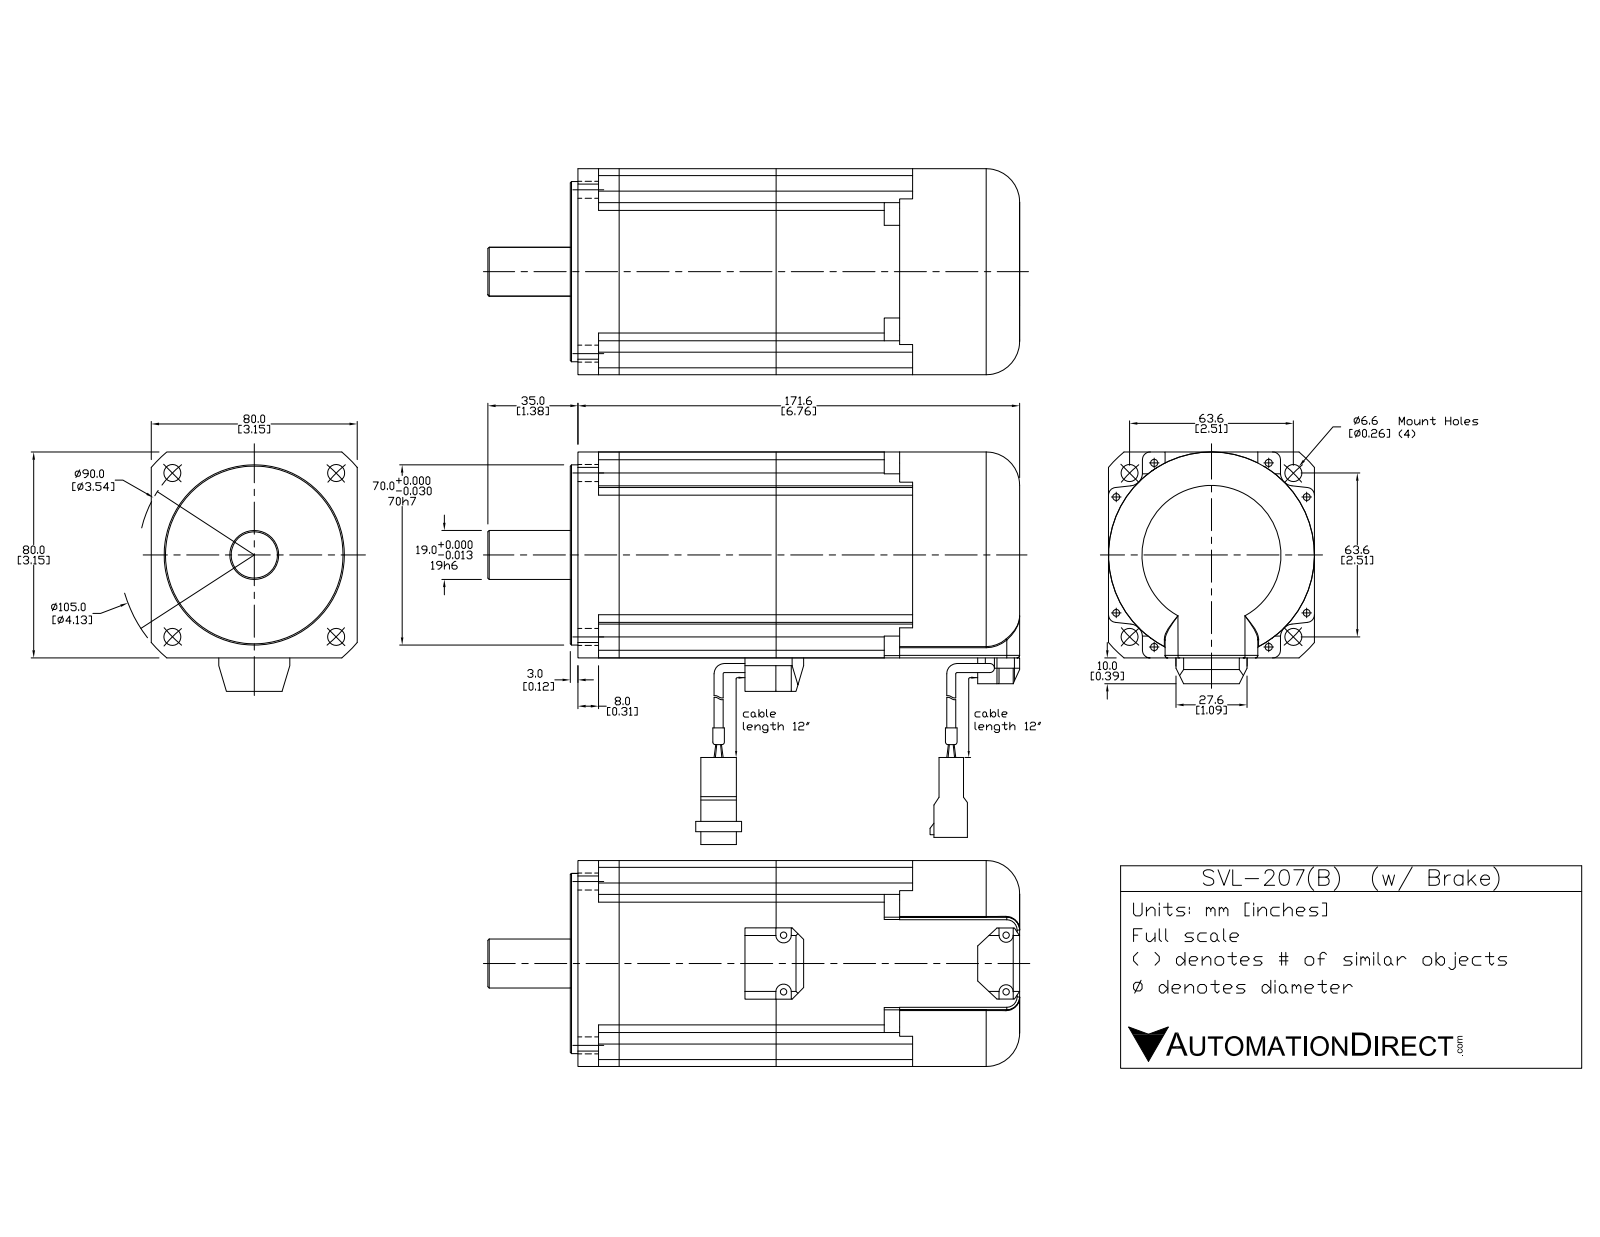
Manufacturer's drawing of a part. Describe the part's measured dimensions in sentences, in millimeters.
The part is named "SVL-207B". Its 3-D file was written by "SolidWorks 2015 (AUTOMOTIVE_DESIGN)". It is 18 solids with 415 faces: 265 planar, 113 cylindrical and 37 other. Overall it measures 208.6 by 93.4 by 80 millimeters. Its volume is 975 080 cubic millimeters and its surface area 105 412 square millimeters. Round holes: 4 of diameter 6.6, 1 of diameter 22. Round bosses or shafts: 8 of diameter 5, 5 of diameter 7, 1 of diameter 80, 1 of diameter 70, 1 of diameter 19, 1 of diameter 5.5. Partial cylindrical surfaces (rounded edges, fillets, slot ends): 14 of radius 1, 12 of radius 3, 4 of radius 2, 4 of radius 2.75, 4 of radius 5, 1 of radius 52.5. The main face-to-face distances are 80, 61, 47.6, 108.6, 66.8, 13.2, 47, 94.6, 155.6, 19. The hole center spacings are 45, 63.64, 90.
